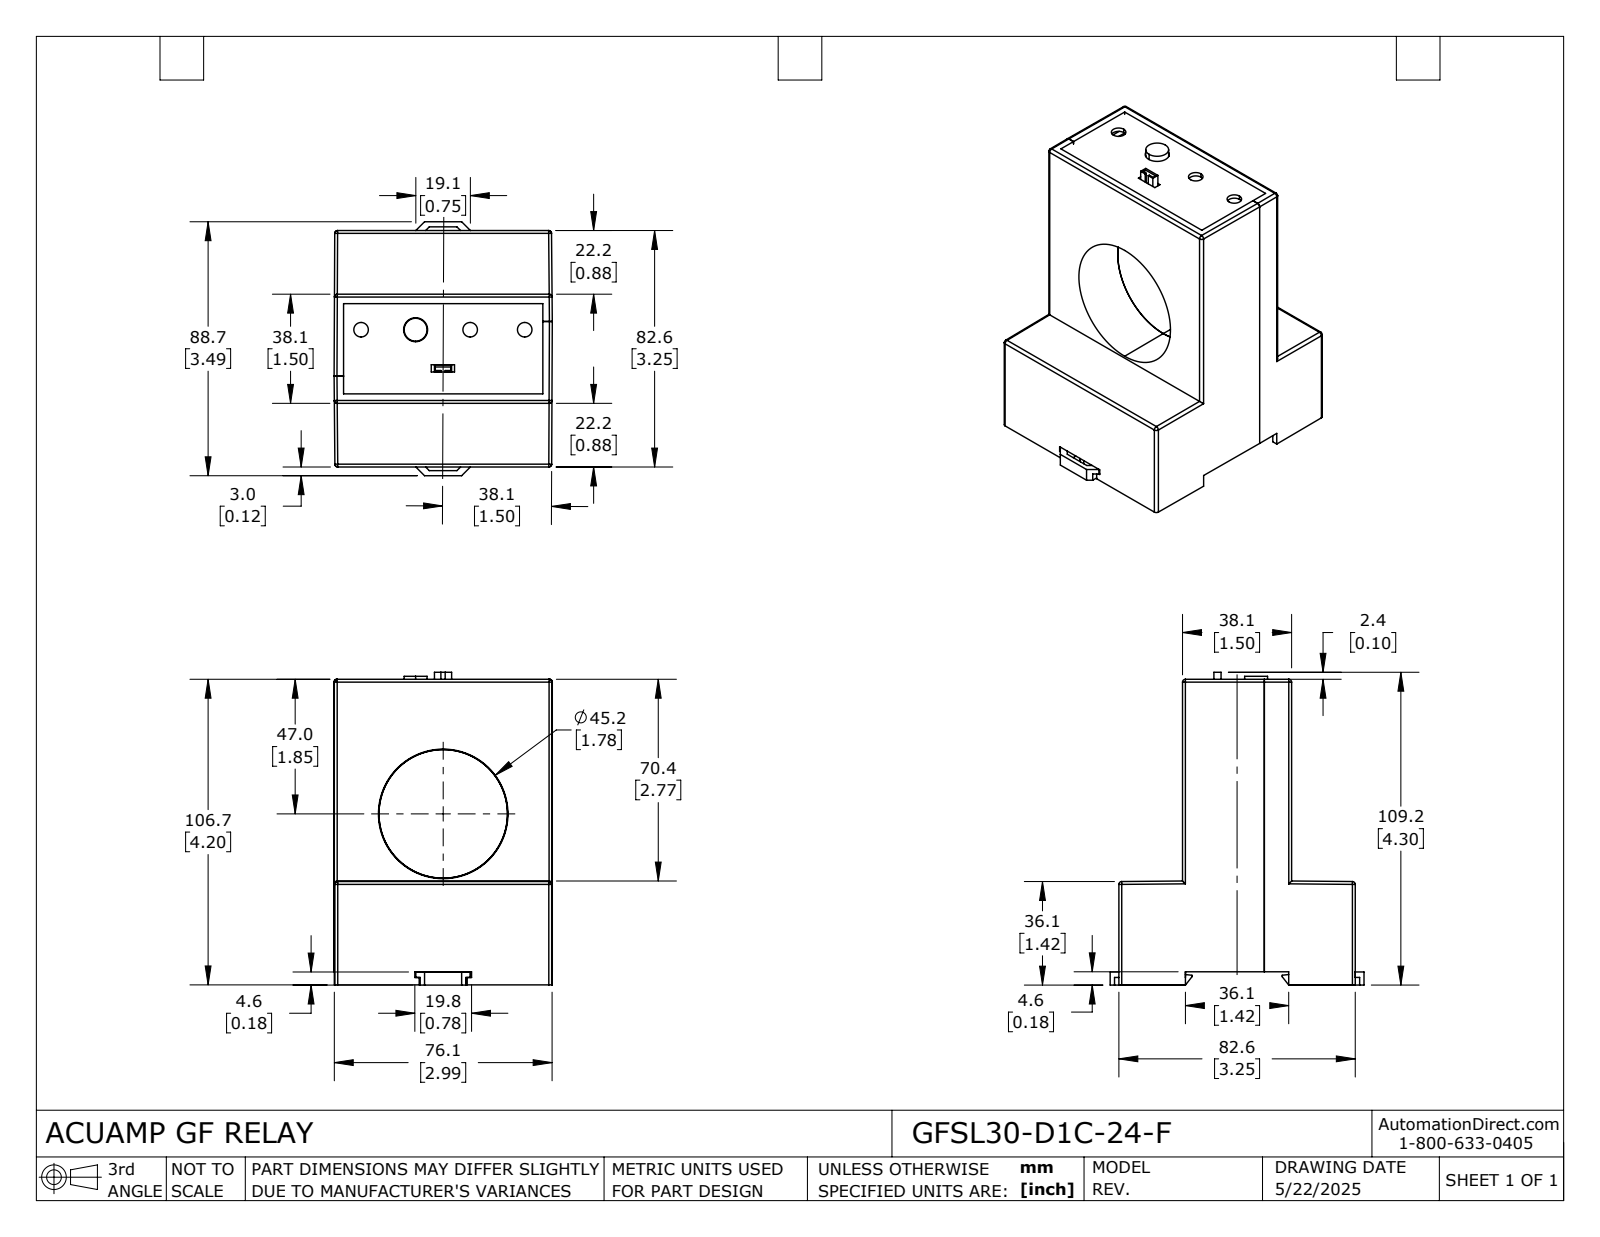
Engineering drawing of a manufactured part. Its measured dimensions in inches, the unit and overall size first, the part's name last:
Units: inches
Overall size (bounding box): 4.299 × 3.49 × 3
Round holes (diameter × count): ⌀0.2 ×7, ⌀0.33 ×4, ⌀0.12 ×2
Round bosses / shafts (diameter × count): ⌀0.1 ×2, ⌀0.315 ×1
Partial cylindrical surfaces — rounded edges, fillets, slot ends (radius × count): R0.02 ×23, R0.039 ×20, R0.008 ×4, R0.012 ×4, R0.104 ×4, R0.18 ×4
Main face-to-face distances: 0.08, 0.875, 2.295, 1.42, 2.916, 0.08, 2.996, 1.5, 0.795, 2.215
Hole centre spacings: 0.75, 0.919, 1.5, 0.531, 1.591, 2.25, 2.312, 0.993
Volume: 5.534 in³ · Surface area: 153.9 in²
Bodies: 8 solids, 1046 faces (890 planar, 120 cylindrical, 36 other)
Part name (STEP PRODUCT): GFSL30-D1C-24-F
STEP written by: SolidWorks 2024 (AUTOMOTIVE_DESIGN)
